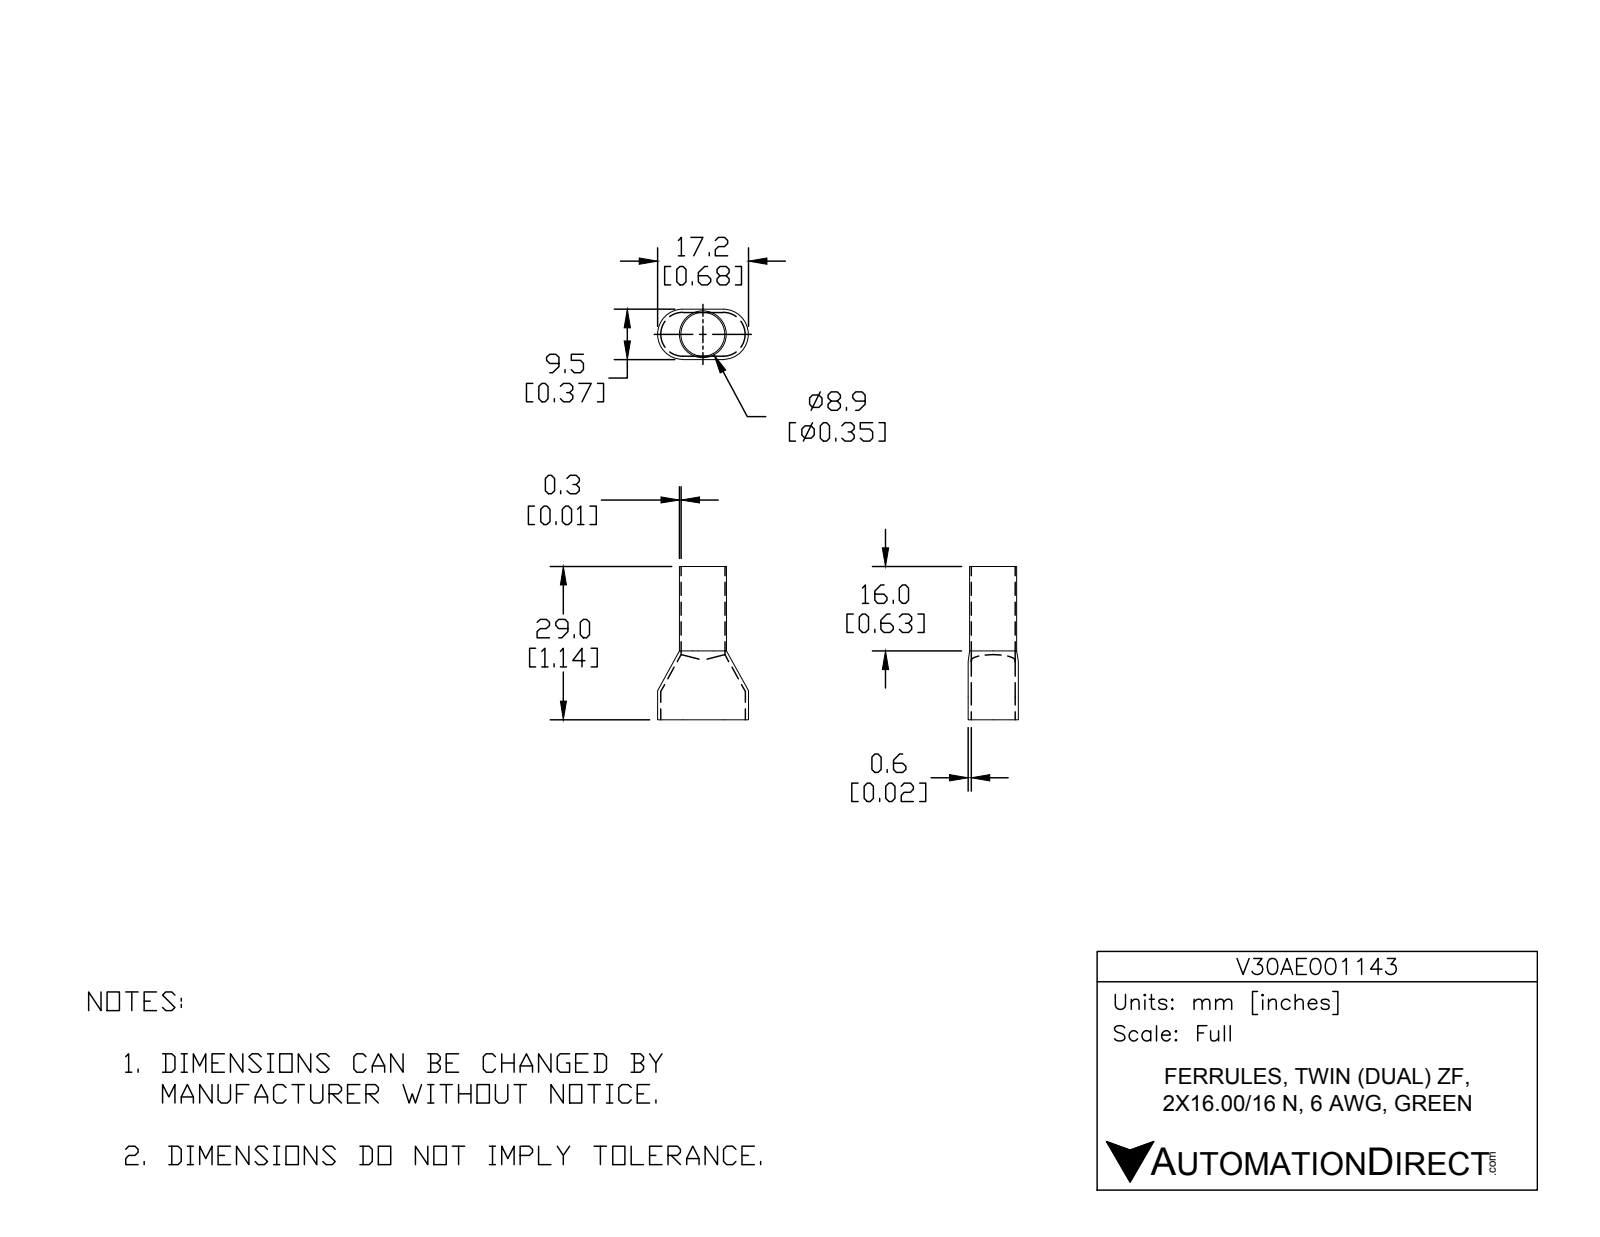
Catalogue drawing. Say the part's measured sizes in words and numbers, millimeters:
The part is named "V30AE001143". Its 3-D file was written by "SolidWorks 2017 (AUTOMOTIVE_DESIGN)". It is 2 solids with 36 faces: 14 planar, 22 cylindrical and 0 other. Overall it measures 29 by 17.2 by 9.5 millimeters. Its volume is 432 cubic millimeters and its surface area 1 937 square millimeters. Round holes: 1 of diameter 8.3. Round bosses or shafts: 1 of diameter 8.9. Partial cylindrical surfaces (rounded edges, fillets, slot ends): 5 of radius 4.15, 5 of radius 4.75. The main face-to-face distances are 0.6, 8.9, 9.5, 8.3, 13, 29, 16.
